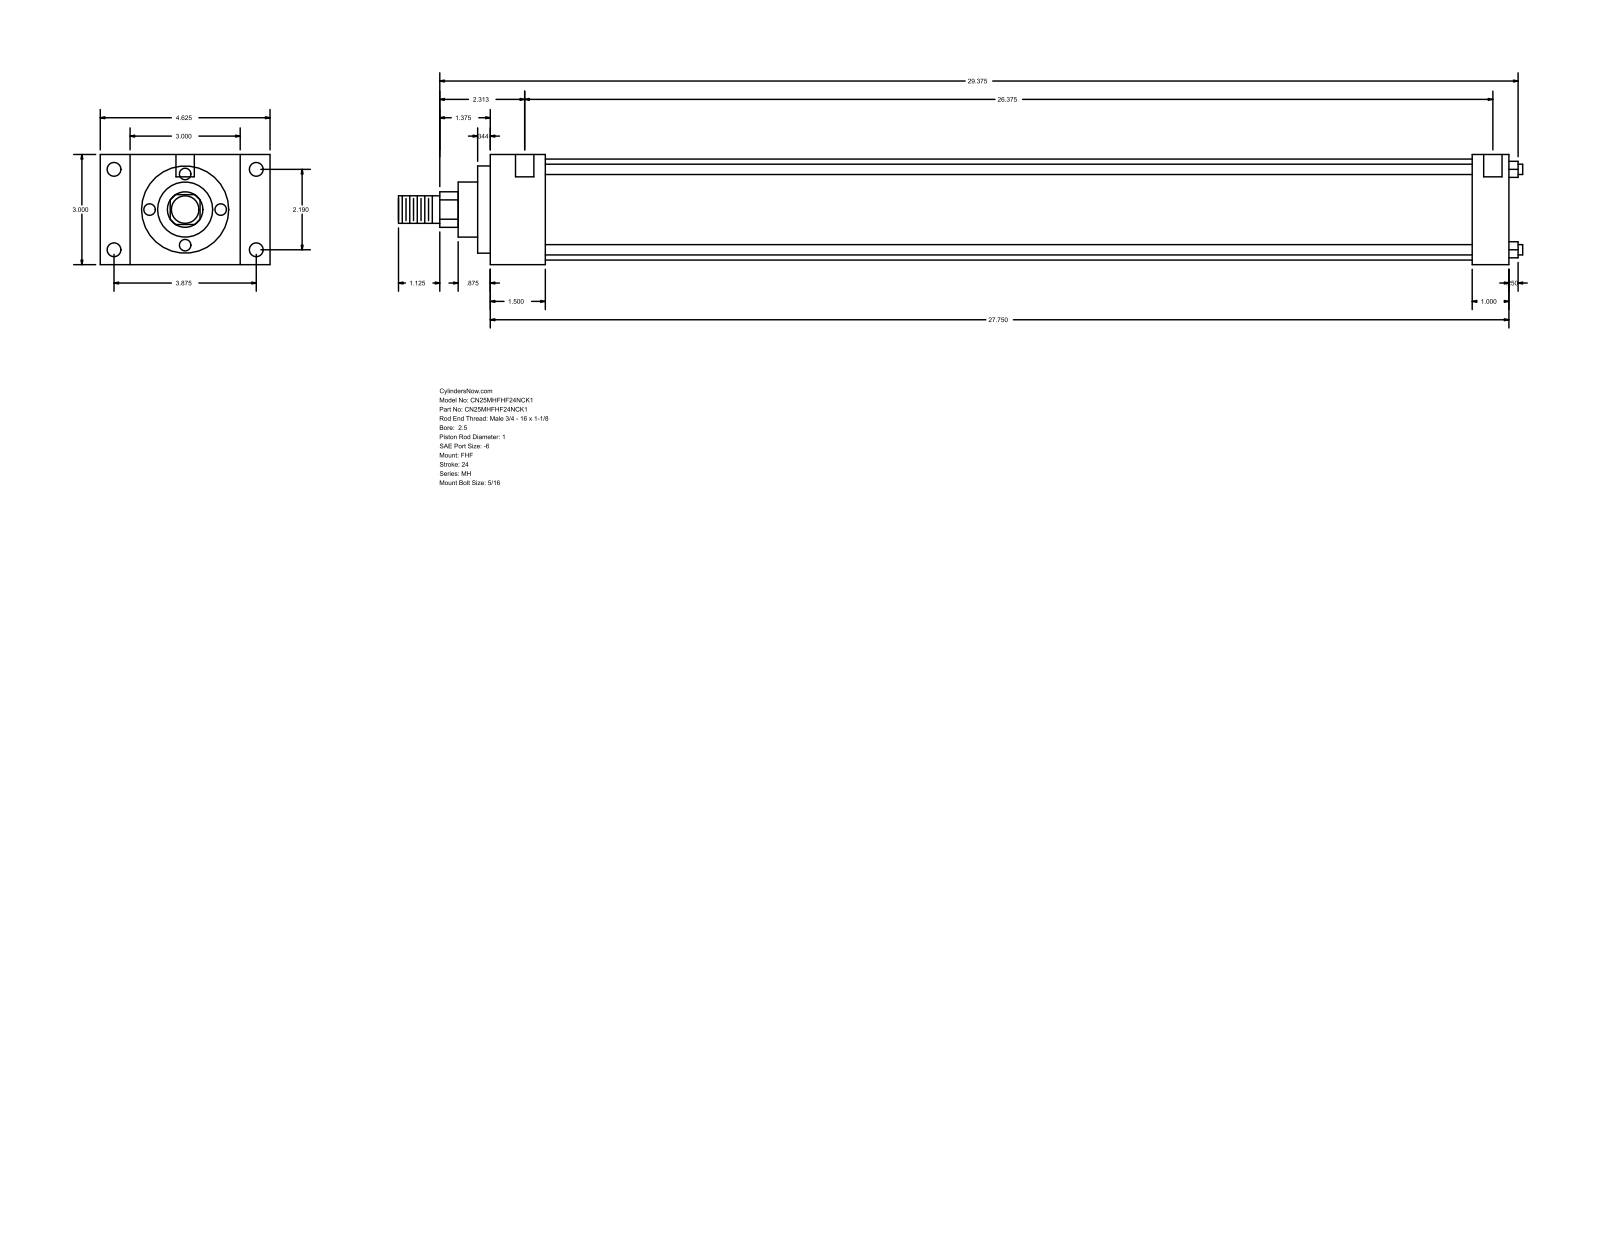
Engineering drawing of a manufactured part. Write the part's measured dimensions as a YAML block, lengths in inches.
part_name: "MH_FHF__0250_1"
step_written_by: "GSSL Pune (CONFIG_CONTROL_DESIGN)"
units: inches
bodies: {solids: 0, faces: 90, planar: 61, cylindrical: 29, other: 0}
overall_size: [30.625, 4.625, 3]
round_holes:
  - {diameter: 0.219, count: 4}
  - {diameter: 0.375, count: 4}
  - {diameter: 0.5, count: 2}
round_bosses_or_shafts:
  - {diameter: 0.281, count: 4}
  - {diameter: 2.75, count: 1}
  - {diameter: 2.375, count: 1}
  - {diameter: 1.5, count: 1}
  - {diameter: 1, count: 1}
  - {diameter: 0.75, count: 1}
partial_cylinders:
  - {radius: 0.484, count: 1}
face_to_face_distances: [3, 27.75, 1.5, 26.25, 0.813, 3.813, 4.625, 1, 26.75, 25.25]
hole_center_spacings: [2.19, 3.875, 4.451, 26.687, 0.125, 0.187, 26.375, 26.5]
